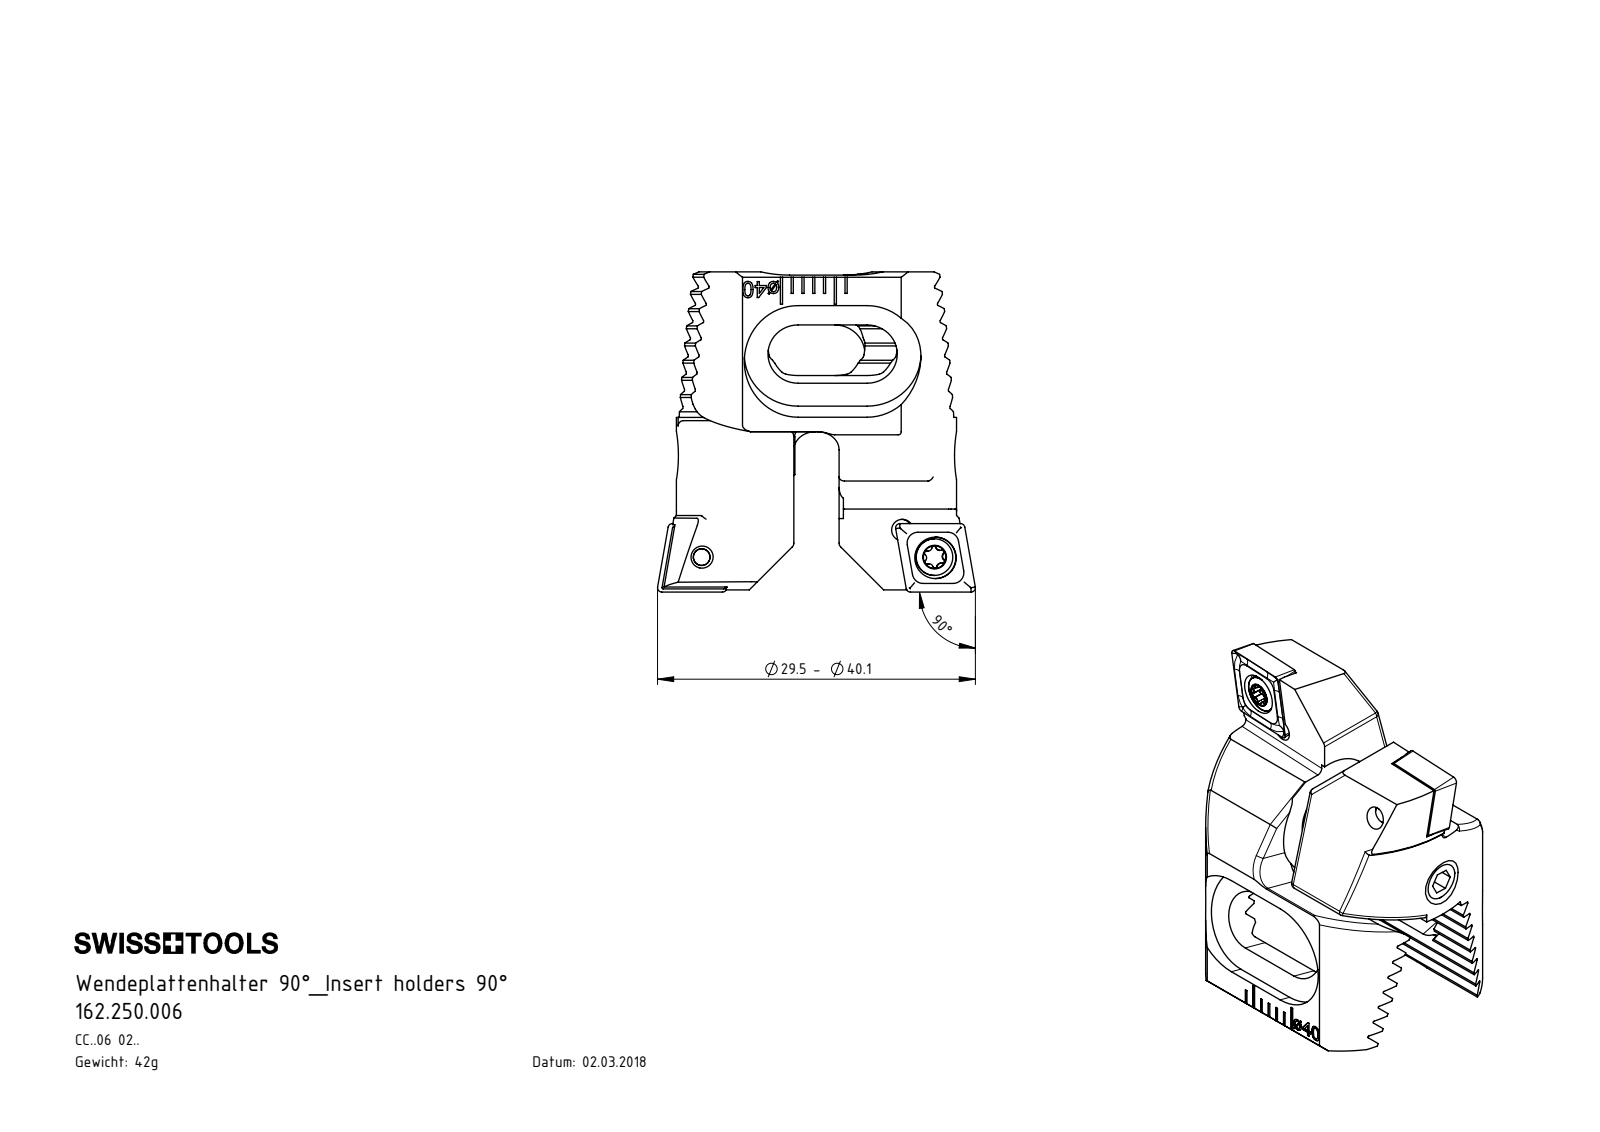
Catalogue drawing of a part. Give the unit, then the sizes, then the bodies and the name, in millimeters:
Units: millimetres
Overall size (bounding box): 29.7 × 29.5 × 20.29
Round holes (diameter × count): ⌀1.6 ×2, ⌀2 ×2, ⌀2.05 ×2, ⌀2.8 ×2, ⌀3.85 ×2, ⌀3.5 ×1
Round bosses / shafts (diameter × count): ⌀3.4 ×2, ⌀2.5 ×2, ⌀4 ×1
Partial cylindrical surfaces — rounded edges, fillets, slot ends (radius × count): R0.5 ×18, R0.12 ×16, R0.21 ×12, R0.36 ×10, R2 ×4, R2.8 ×4, R5 ×4, R12 ×4
Main face-to-face distances: 1.43, 2.86, 4.29, 5.72, 7.15, 3.9, 4.6, 8.58, 10, 0.4
Hole centre spacings: 3.91, 4.01, 7, 19.06, 19.15, 21.97, 13.52, 15.9
Volume: 5 290 mm³ · Surface area: 4 875 mm²
Bodies: 9 solids, 672 faces (313 planar, 157 cylindrical, 202 other)
Part name (STEP PRODUCT): ZC2-xxx.001.016_A; CCMT060204; Z25-ER3.001.010_A; WCA-ER2.001.006_A (+2 more)
STEP written by: SolidWorks 2017 (CONFIG_CONTROL_DESIGN)
